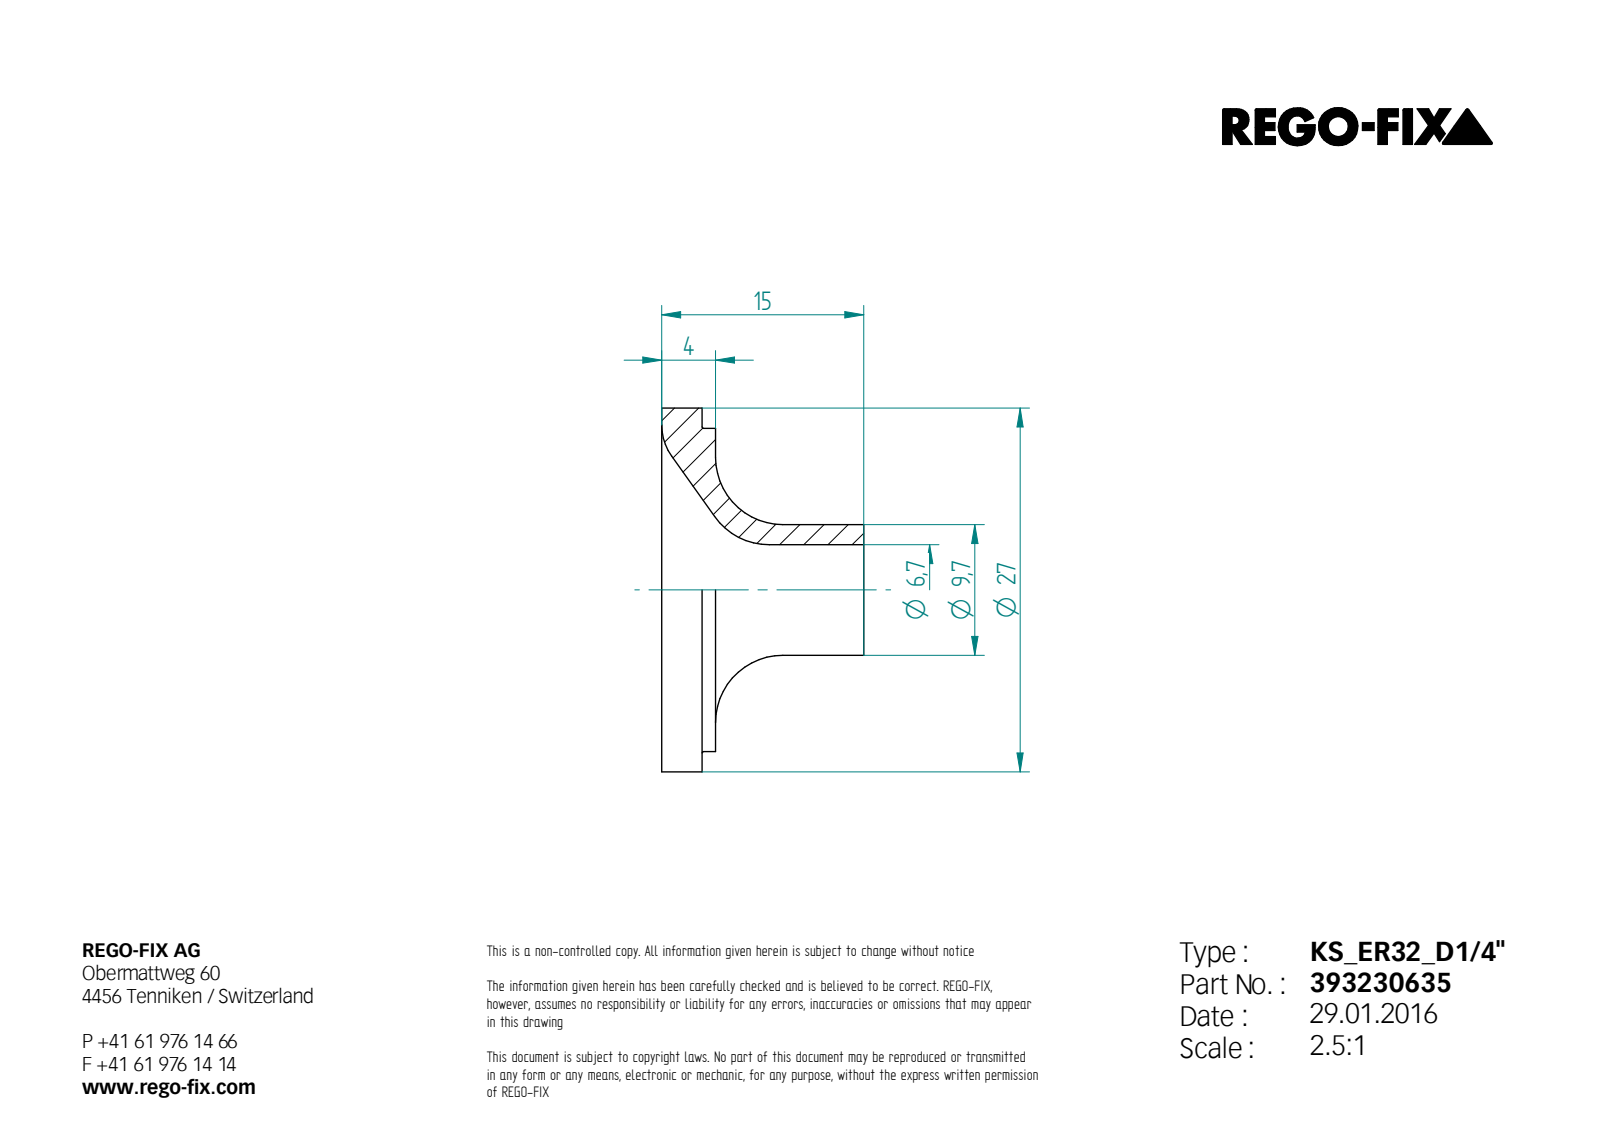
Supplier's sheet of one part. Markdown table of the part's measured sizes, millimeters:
| quantity | value |
| --- | --- |
| STEP written by | Unknown (AUTOMOTIVE_DESIGN) |
| units | millimeters |
| bodies | 1 solid, 13 faces (4 planar, 4 cylindrical, 5 other) |
| overall size | 27 × 27 × 15 |
| volume | 1 856 mm³ |
| surface area | 1 953 mm² |
| round holes (diameter × count) | 6.7 × 1 |
| round bosses / shafts (diameter × count) | 27 × 1, 24 × 1, 9.7 × 1 |
| main face-to-face distances | 1, 3, 4, 15, 12, 11 |
